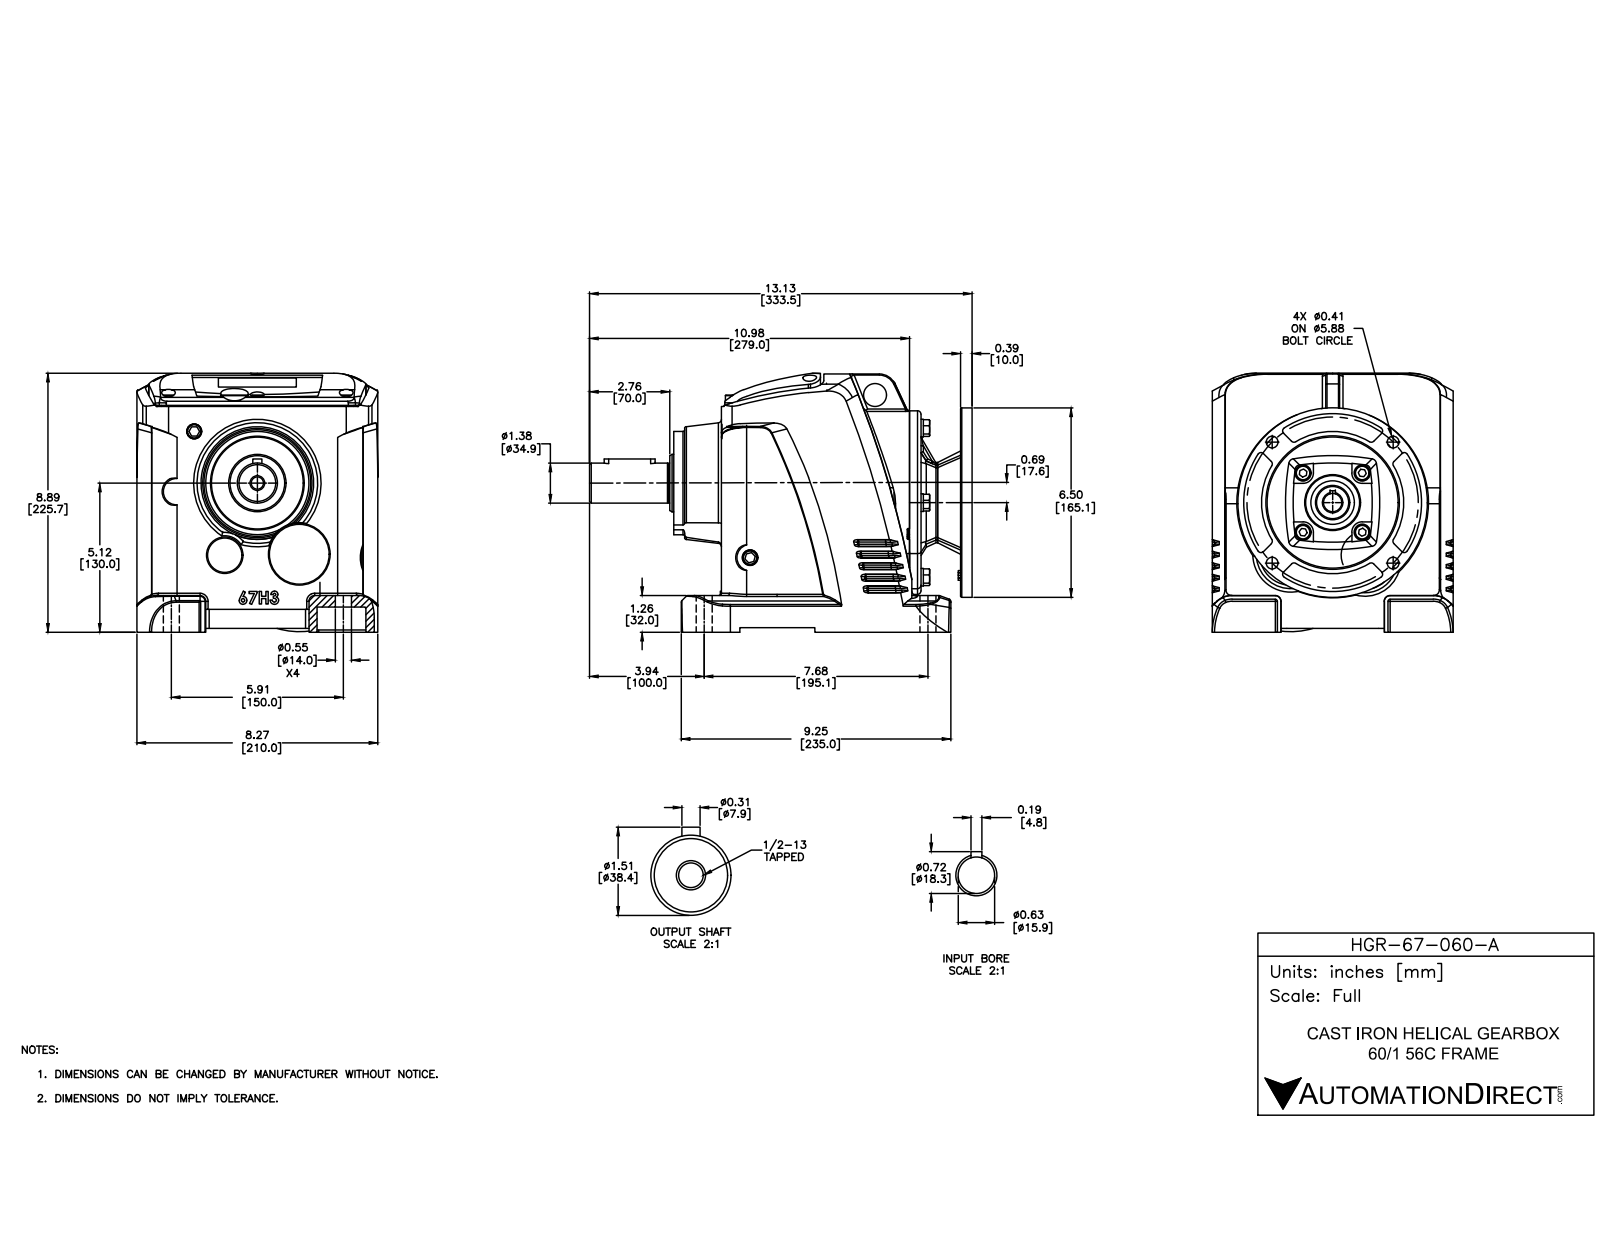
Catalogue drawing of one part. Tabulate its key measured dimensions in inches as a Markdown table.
| quantity | value |
| --- | --- |
| part name | HGR-67-060-A |
| STEP written by | SolidWorks 2015 (CONFIG_CONTROL_DESIGN) |
| units | inches |
| bodies | 16 solids, 1073 faces (356 planar, 279 cylindrical, 438 other) |
| overall size | 13.13 × 8.889 × 8.268 |
| volume | 409.4 in³ |
| surface area | 797.7 in² |
| round holes (diameter × count) | 0.472 × 6, 0.406 × 4, 0.55 × 4, 0.551 × 4, 0.422 × 1, 0.625 × 1, 0.787 × 1, 1.969 × 1, 4.5 × 1 |
| round bosses / shafts (diameter × count) | 0.606 × 4, 0.512 × 4, 0.495 × 4, 0.394 × 3, 1.181 × 2, 6.5 × 1, 6.299 × 1, 3.543 × 1 |
| partial cylindrical surfaces (radius × count) | 0.079 × 45, 0.118 × 21, 0.197 × 7, 0.039 × 4, 0.354 × 4, 0.787 × 4, 0.512 × 3, 0.156 × 2 |
| main face-to-face distances | 0.394, 0.512, 1.752, 0.039, 7.756, 6.457, 1.358, 8.209, 0.236, 0.059 |
| hole center spacings | 3.27, 1.437, 1.5, 2.032, 2.937, 4.154, 4.374, 1.074 |
